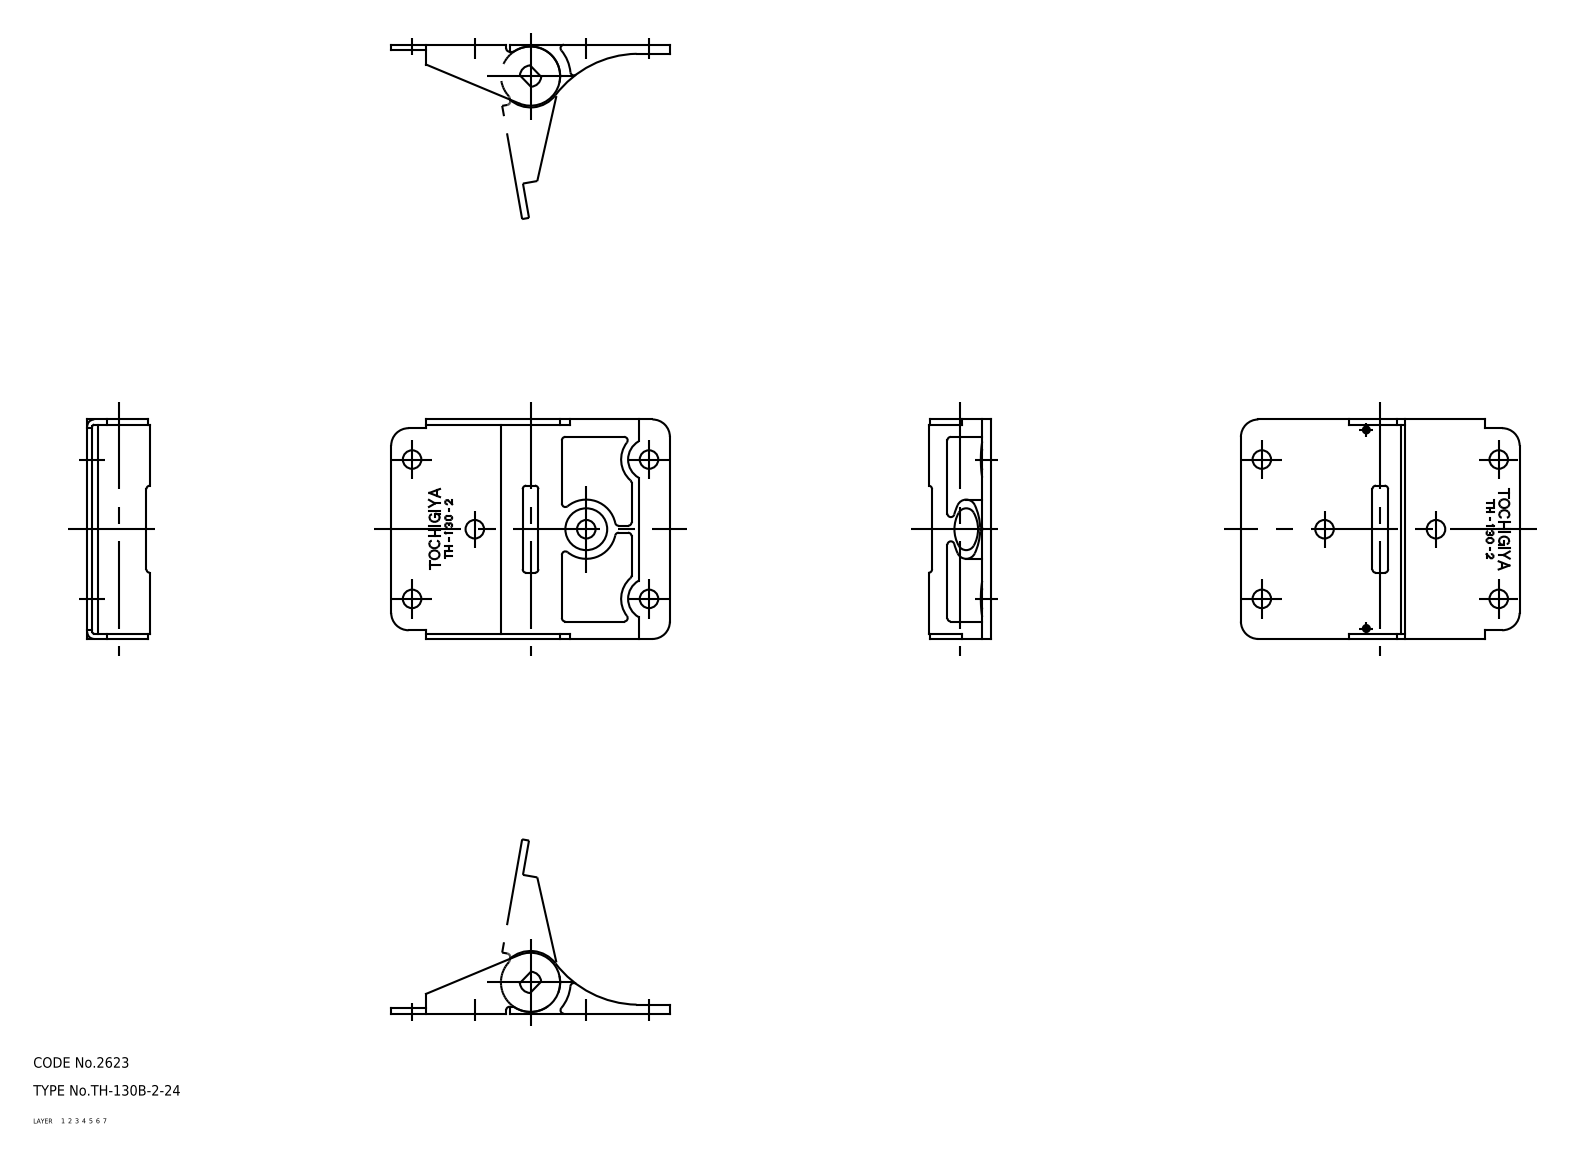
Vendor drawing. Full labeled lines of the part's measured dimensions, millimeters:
Part name (STEP PRODUCT): shaft; hinge piece; TH_130B_2_24_3680_36
STEP written by: CADfix (AUTOMOTIVE_DESIGN)
Units: millimetres
Bodies: 3 solids, 117 faces (0 planar, 0 cylindrical, 117 other)
Overall size (bounding box): 80 × 63 × 18
Volume: 26 390 mm³ · Surface area: 17 160 mm²
